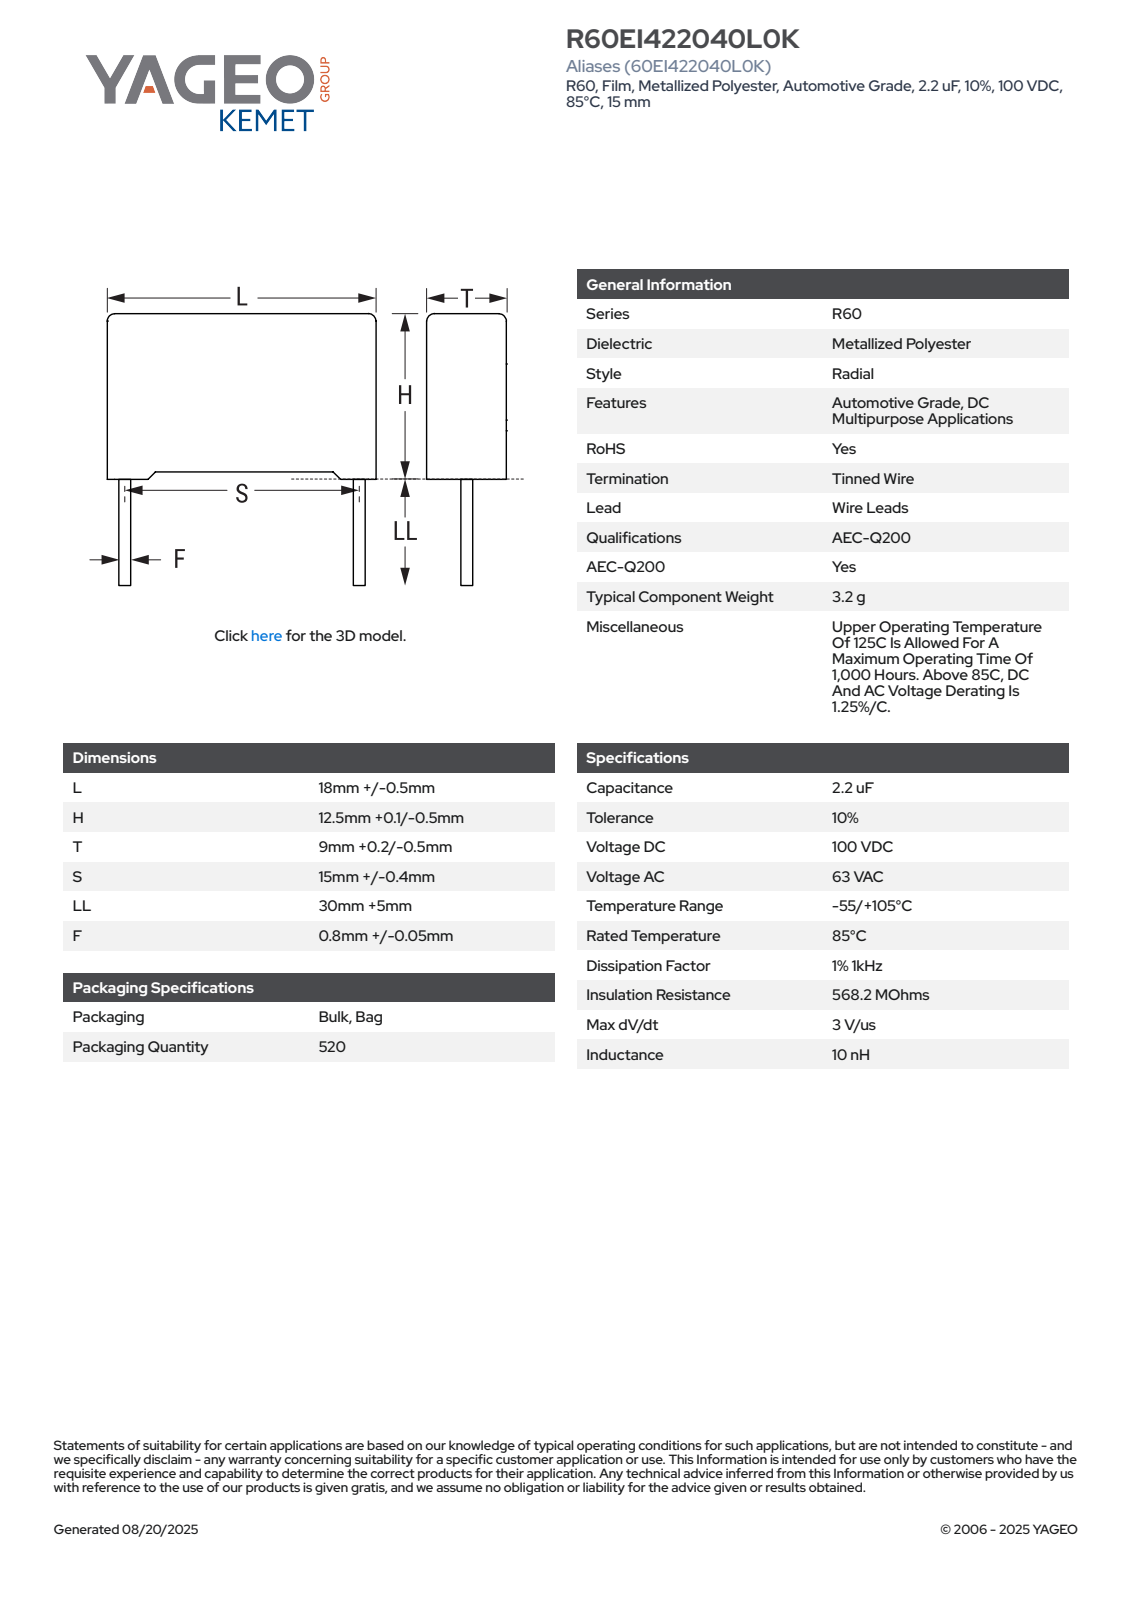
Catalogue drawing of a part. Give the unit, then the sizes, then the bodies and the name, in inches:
Units: inches
Overall size (bounding box): 1.874 × 0.728 × 0.363
Round bosses / shafts (diameter × count): ⌀0.033 ×2
Partial cylindrical surfaces — rounded edges, fillets, slot ends (radius × count): R0.02 ×4
Main face-to-face distances: 0.362, 0.467, 0.728, 0.024, 0.03, 0.496, 0.338, 0.017, 0.013, 0.479
Volume: 0.127 in³ · Surface area: 1.955 in²
Bodies: 4 solids, 85 faces (77 planar, 8 cylindrical, 0 other)
Part name (STEP PRODUCT): CFR_RB2_18X12.5X9_L18.5H12.6T9.2S15LL35F0.85
STEP written by: SolidWorks 2021 (AUTOMOTIVE_DESIGN)
